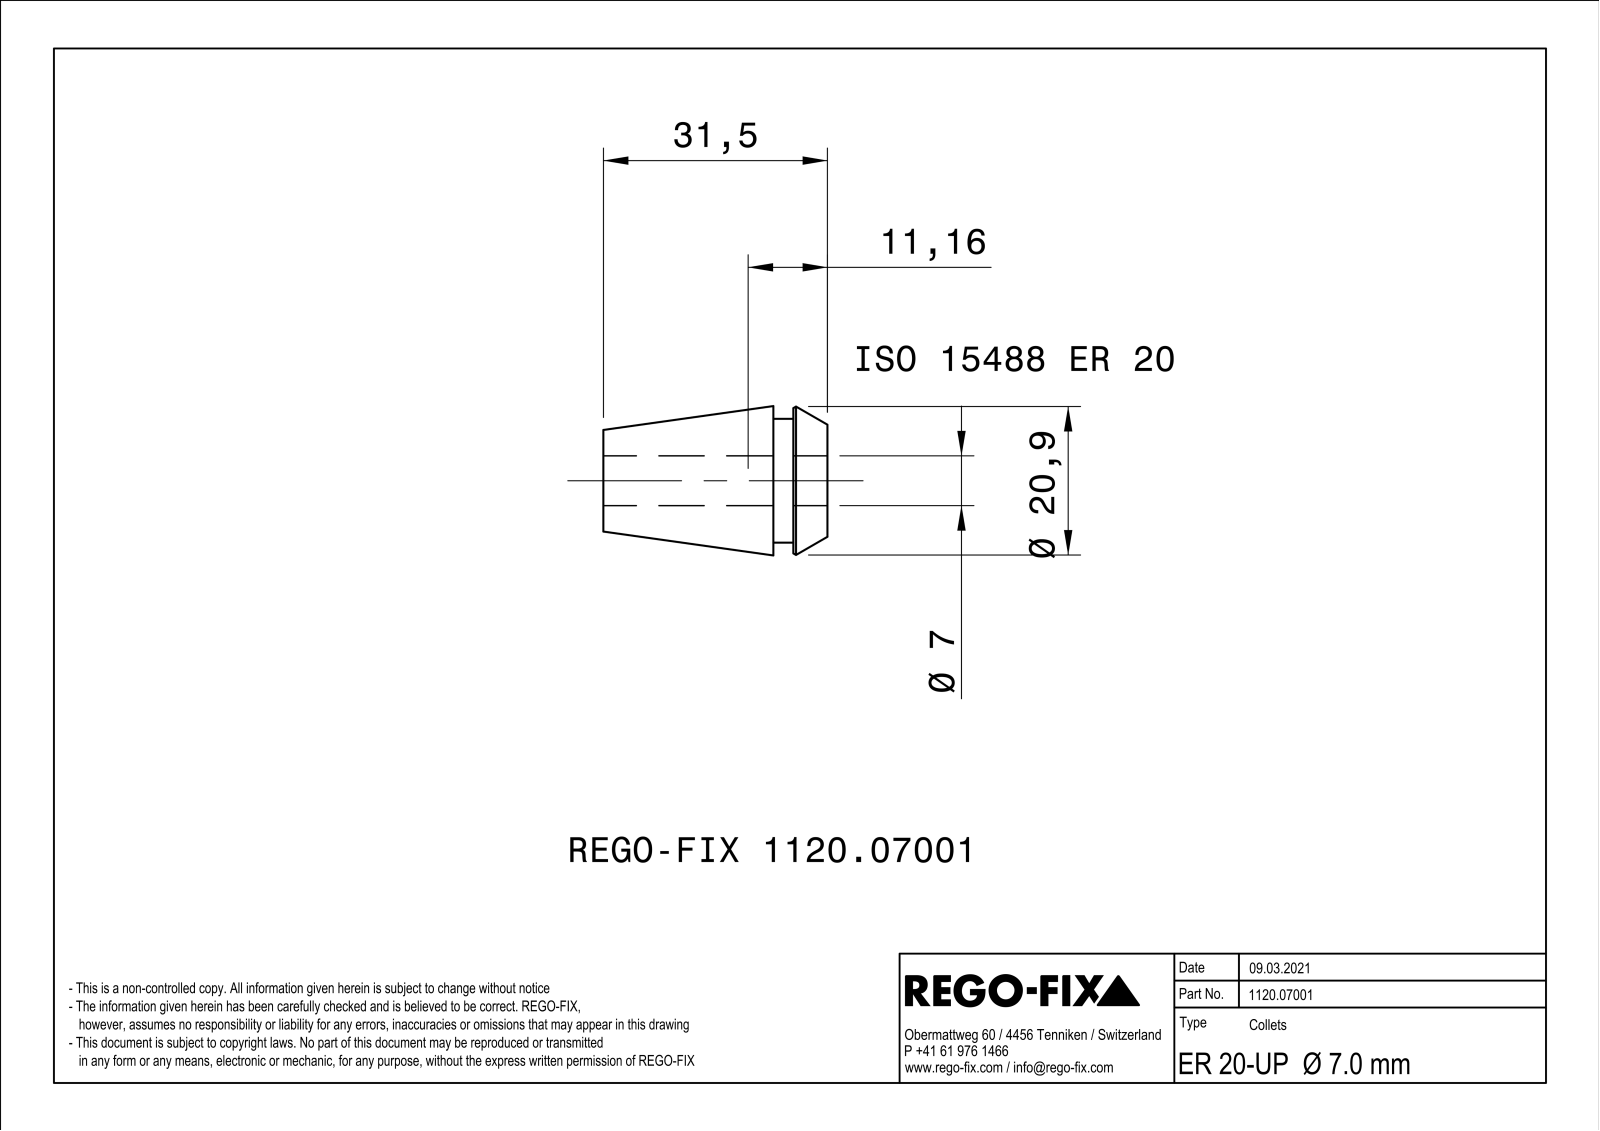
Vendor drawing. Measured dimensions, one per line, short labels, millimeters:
name: NOCUT
written by: SIEMENS PLM Software Solid Edge ST10 (AUTOMOTIVE_DESIGN)
unit: mm
bodies: 1 solid, 177 faces (88 planar, 9 cylindrical, 80 other)
size: 31.5 × 20.99 × 20.99
volume: 5 234 mm³; area: 7 185 mm²
holes: 1× ⌀7
bosses: 1× ⌀17.4
face distances: 0.6, 31.5, 7.6, 23.9, 4.8, 2.8, 26.7, 5.5, 0.7, 2.1
